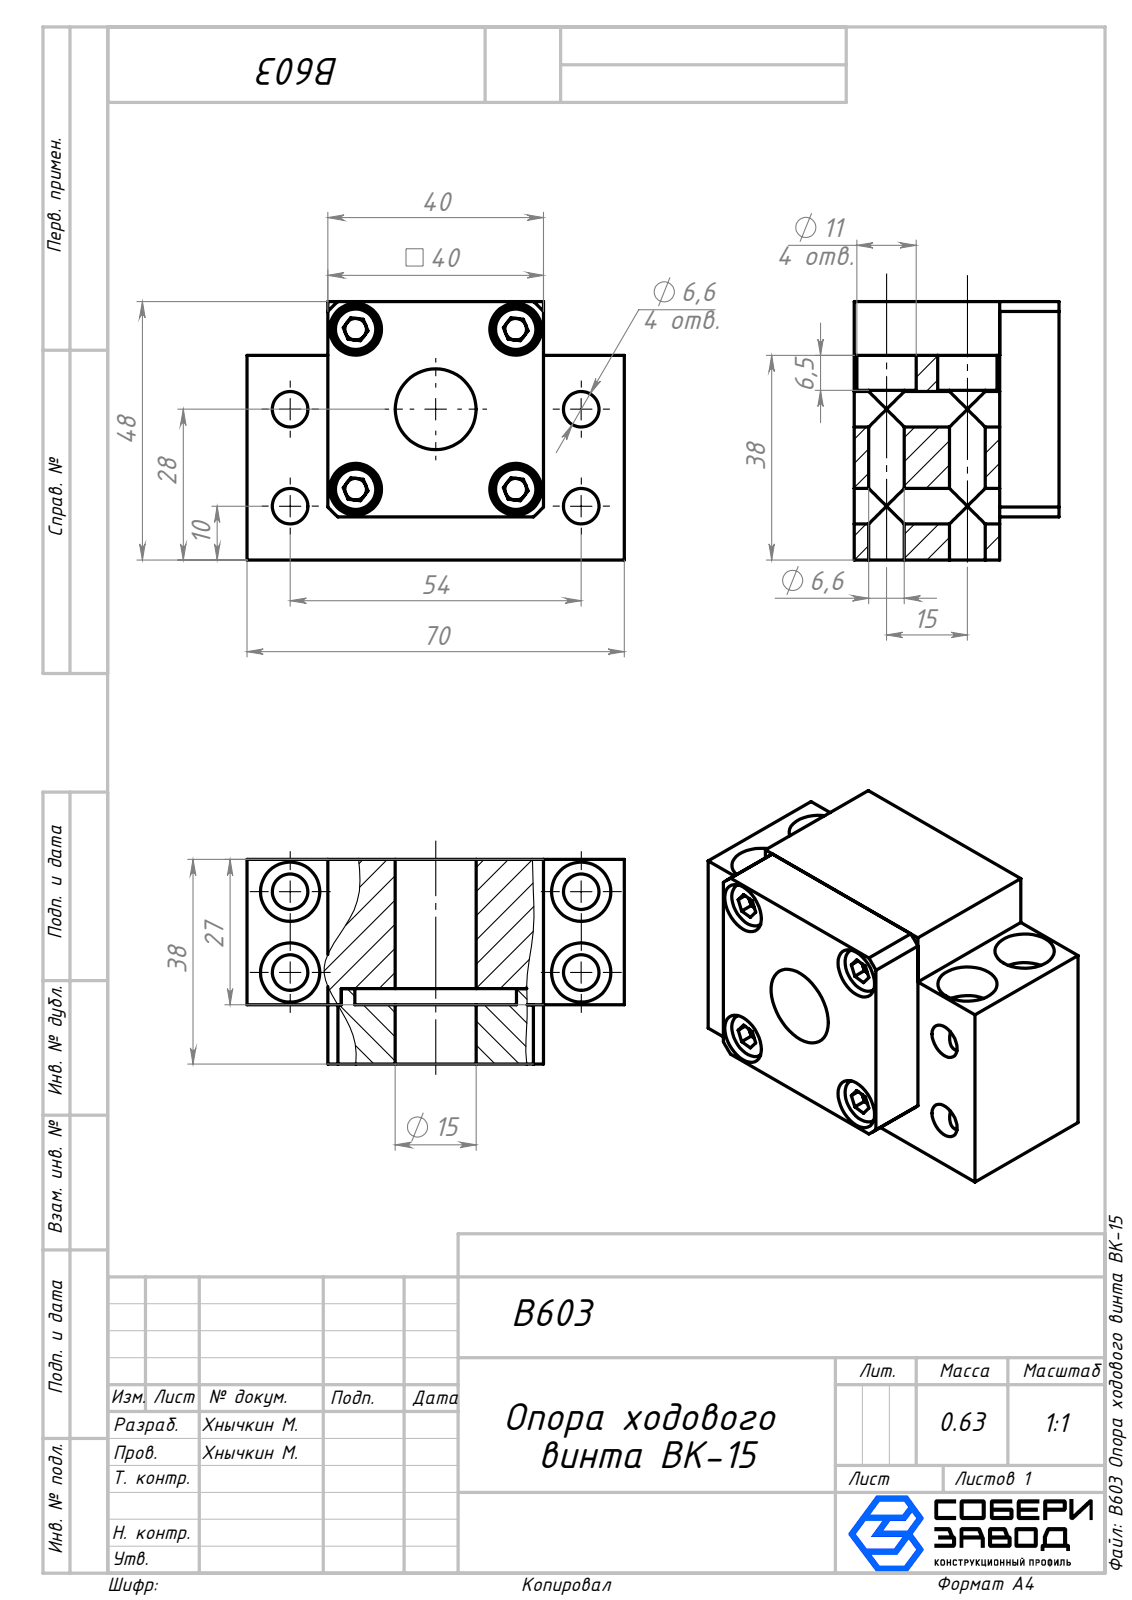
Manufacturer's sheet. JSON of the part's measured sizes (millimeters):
{"part_name": "B603 Корпус опоры ходового винта BK-15_00; socket head cap screw_din_DIN 912 M5 x 16 --- 16N; B603 Крышка_00; B603 Опора ходового винта BK-15", "step_written_by": "SolidWorks 2026 (AUTOMOTIVE_DESIGN)", "units": "millimeters", "bodies": {"solids": 6, "faces": 233, "planar": 91, "cylindrical": 110, "other": 32}, "overall_size": [70, 48, 38], "volume_mm3": 82220, "surface_area_mm2": 26763, "round_holes": [[6.6, 8], [4, 4], [5.4, 4], [9.6, 4], [11, 4], [15, 1], [30, 1], [35, 1]], "round_bosses_or_shafts": [[8.5, 4], [5, 4]], "partial_cylinders_radius": [[27, 1]], "face_to_face_distances": [27, 38, 48, 15, 55, 11, 24, 3, 14, 40], "hole_center_spacings": [19.19, 21, 29.7, 44.41, 54, 12.55, 15, 18]}
